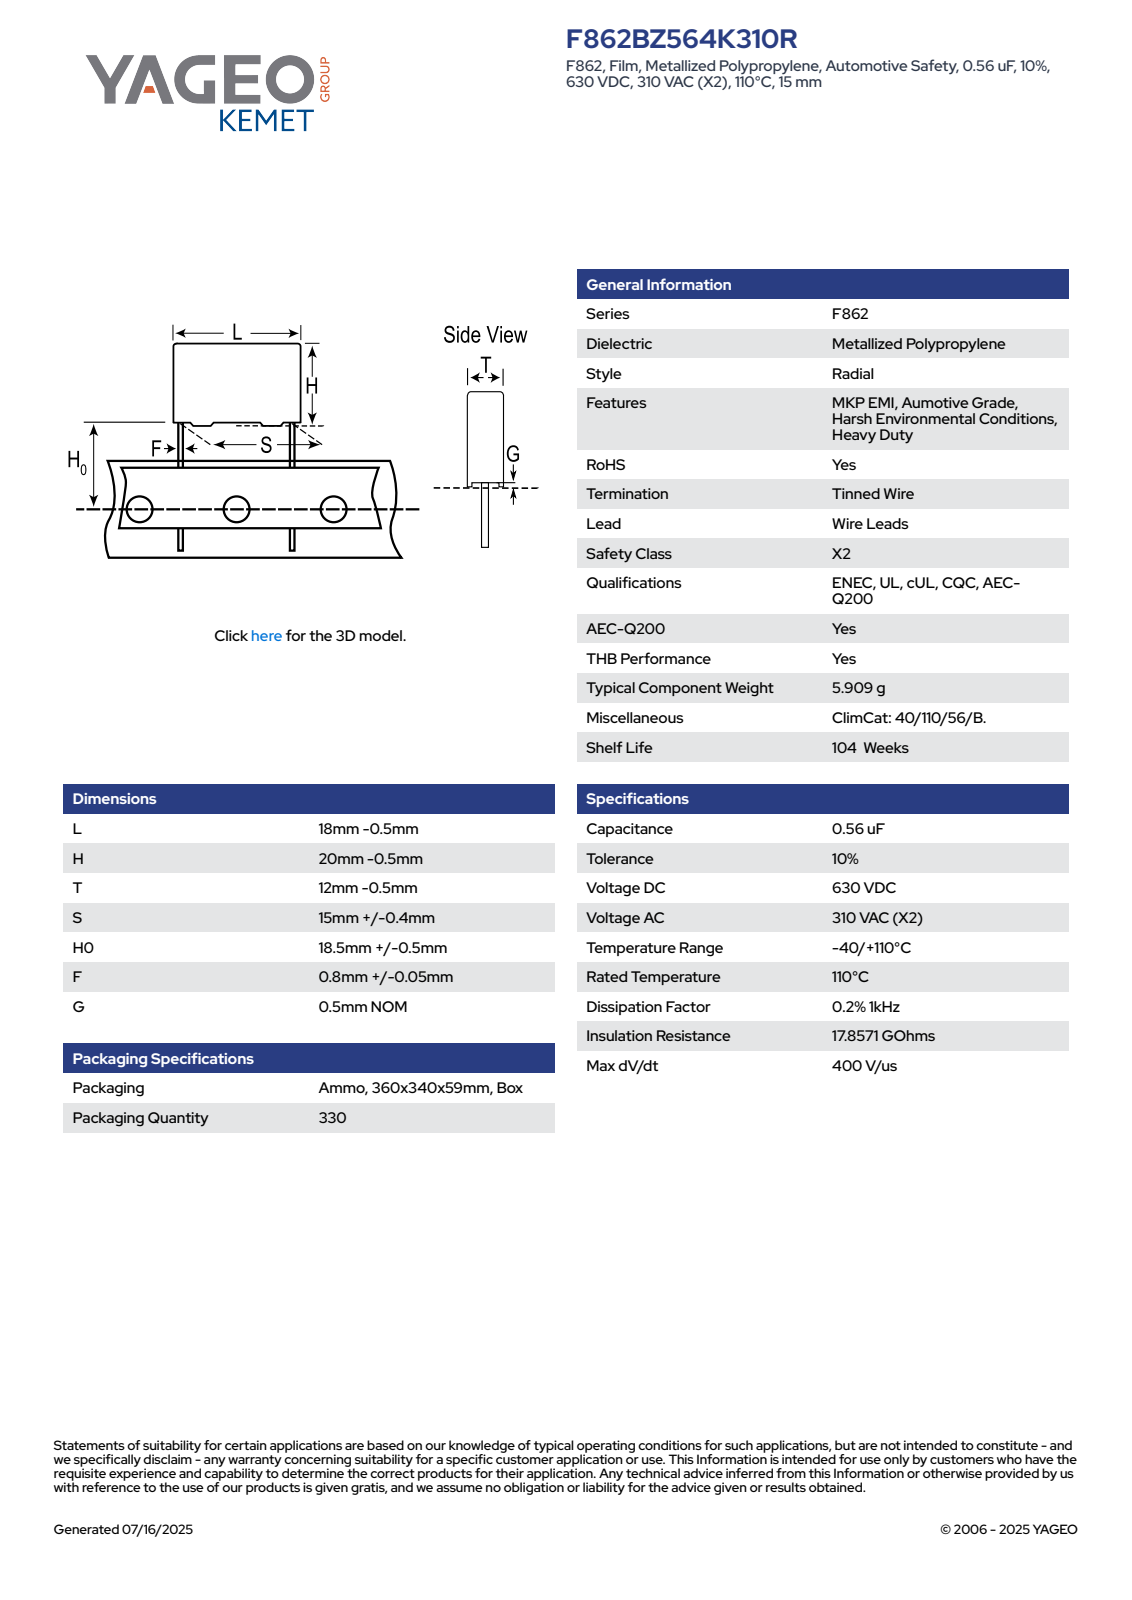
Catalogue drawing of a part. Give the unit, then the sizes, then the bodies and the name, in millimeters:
Units: millimetres
Overall size (bounding box): 38.5 × 17.5 × 11.51
Round bosses / shafts (diameter × count): ⌀0.85 ×2
Partial cylindrical surfaces — rounded edges, fillets, slot ends (radius × count): R0.5 ×4
Main face-to-face distances: 11.5, 17.5, 19, 19.5, 0.5, 0.66, 10.84, 10.18, 38.5, 8.84
Volume: 3 847 mm³ · Surface area: 1 642 mm²
Bodies: 4 solids, 89 faces (81 planar, 8 cylindrical, 0 other)
Part name (STEP PRODUCT): CFR_RBG_18X20X12_L17.5H19.5T11.5S15H019F0.85G0.5
STEP written by: SolidWorks 2014 (AUTOMOTIVE_DESIGN)
